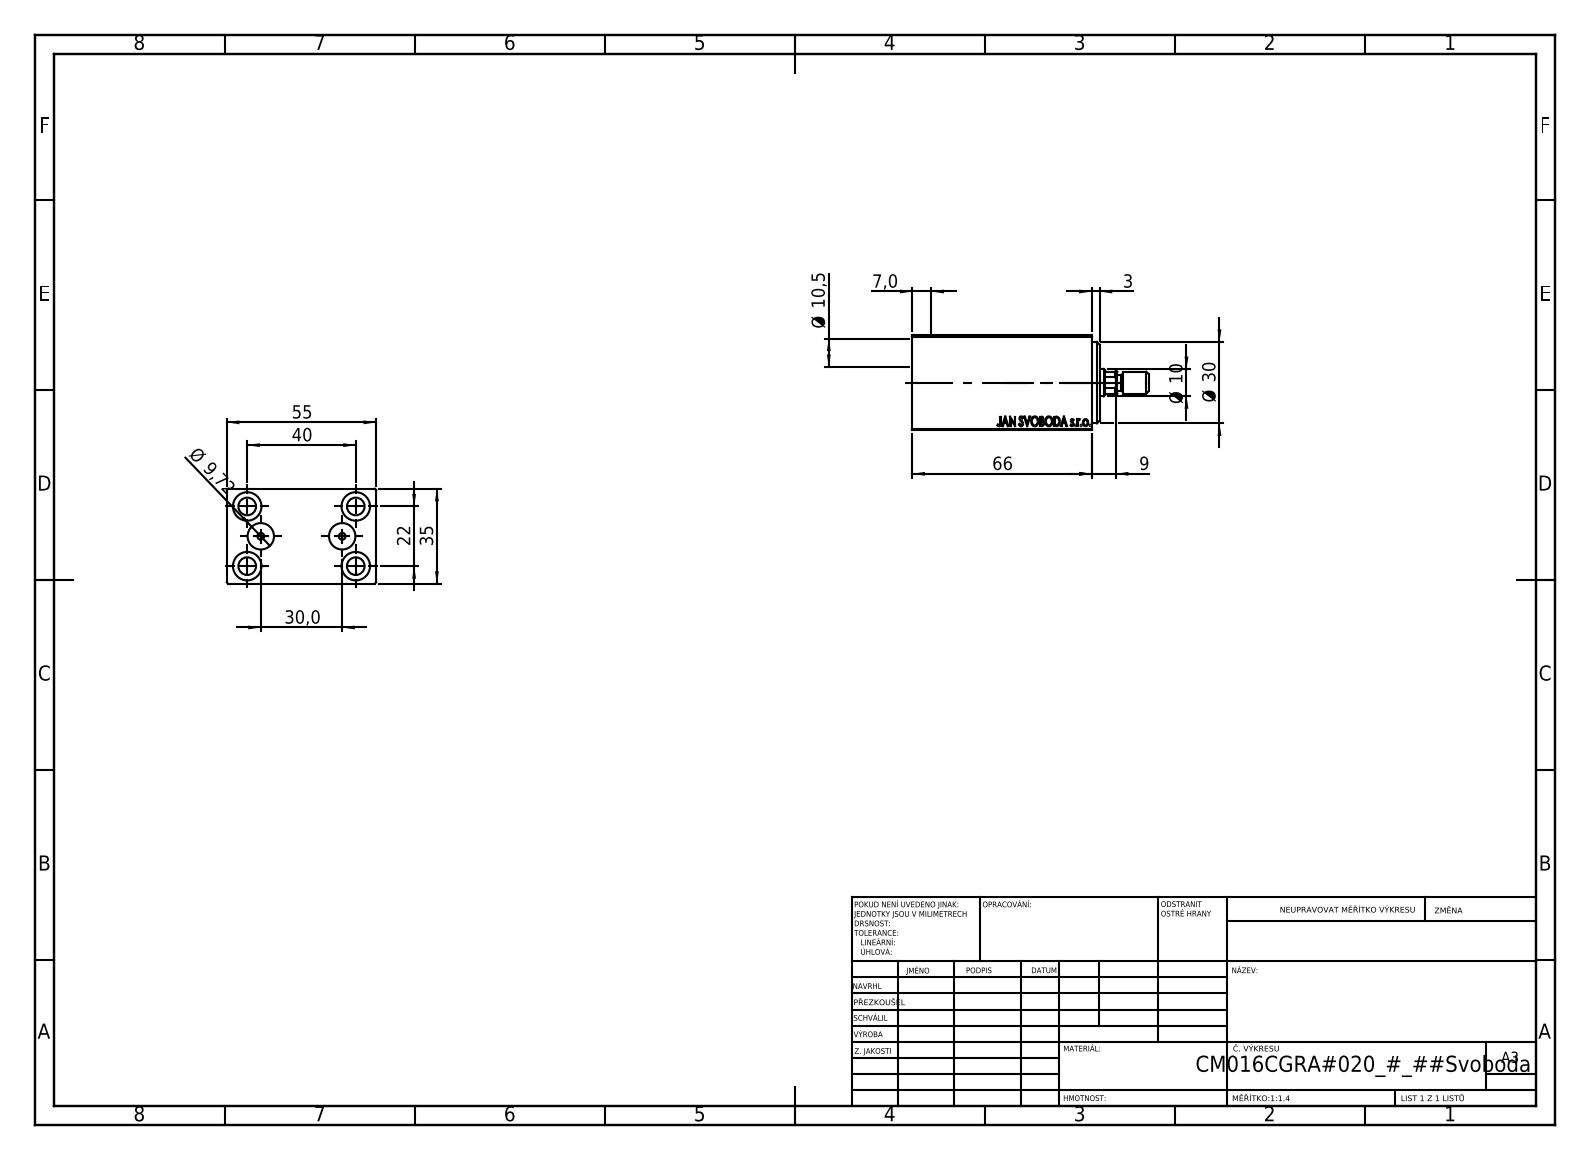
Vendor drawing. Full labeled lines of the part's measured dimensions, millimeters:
Part name (STEP PRODUCT): V450CM_VC_B; V450CM_MALE_METRIC; V450CM_C_Body; V450CM_C_VCP
STEP written by: SolidWorks 2019 (CONFIG_CONTROL_DESIGN)
Units: millimetres
Bodies: 4 solids, 875 faces (413 planar, 62 cylindrical, 400 other)
Overall size (bounding box): 87 × 55 × 35
Volume: 113 485 mm³ · Surface area: 32 637 mm²
Round holes (diameter × count): ⌀6.5 ×4, ⌀10.5 ×4, ⌀2.5 ×2, ⌀9.72 ×2, ⌀4.5 ×1, ⌀10 ×1, ⌀13.5 ×1, ⌀14.5 ×1, ⌀16 ×1, ⌀18 ×1, ⌀30 ×1
Round bosses / shafts (diameter × count): ⌀8 ×1, ⌀6 ×1
Partial cylindrical surfaces — rounded edges, fillets, slot ends (radius × count): R4.5 ×1
Main face-to-face distances: 35, 55, 5, 61, 66, 2, 3, 59, 56, 8
Hole centre spacings: 12.08, 22.83, 36.69, 15, 22, 40, 45.65, 30
